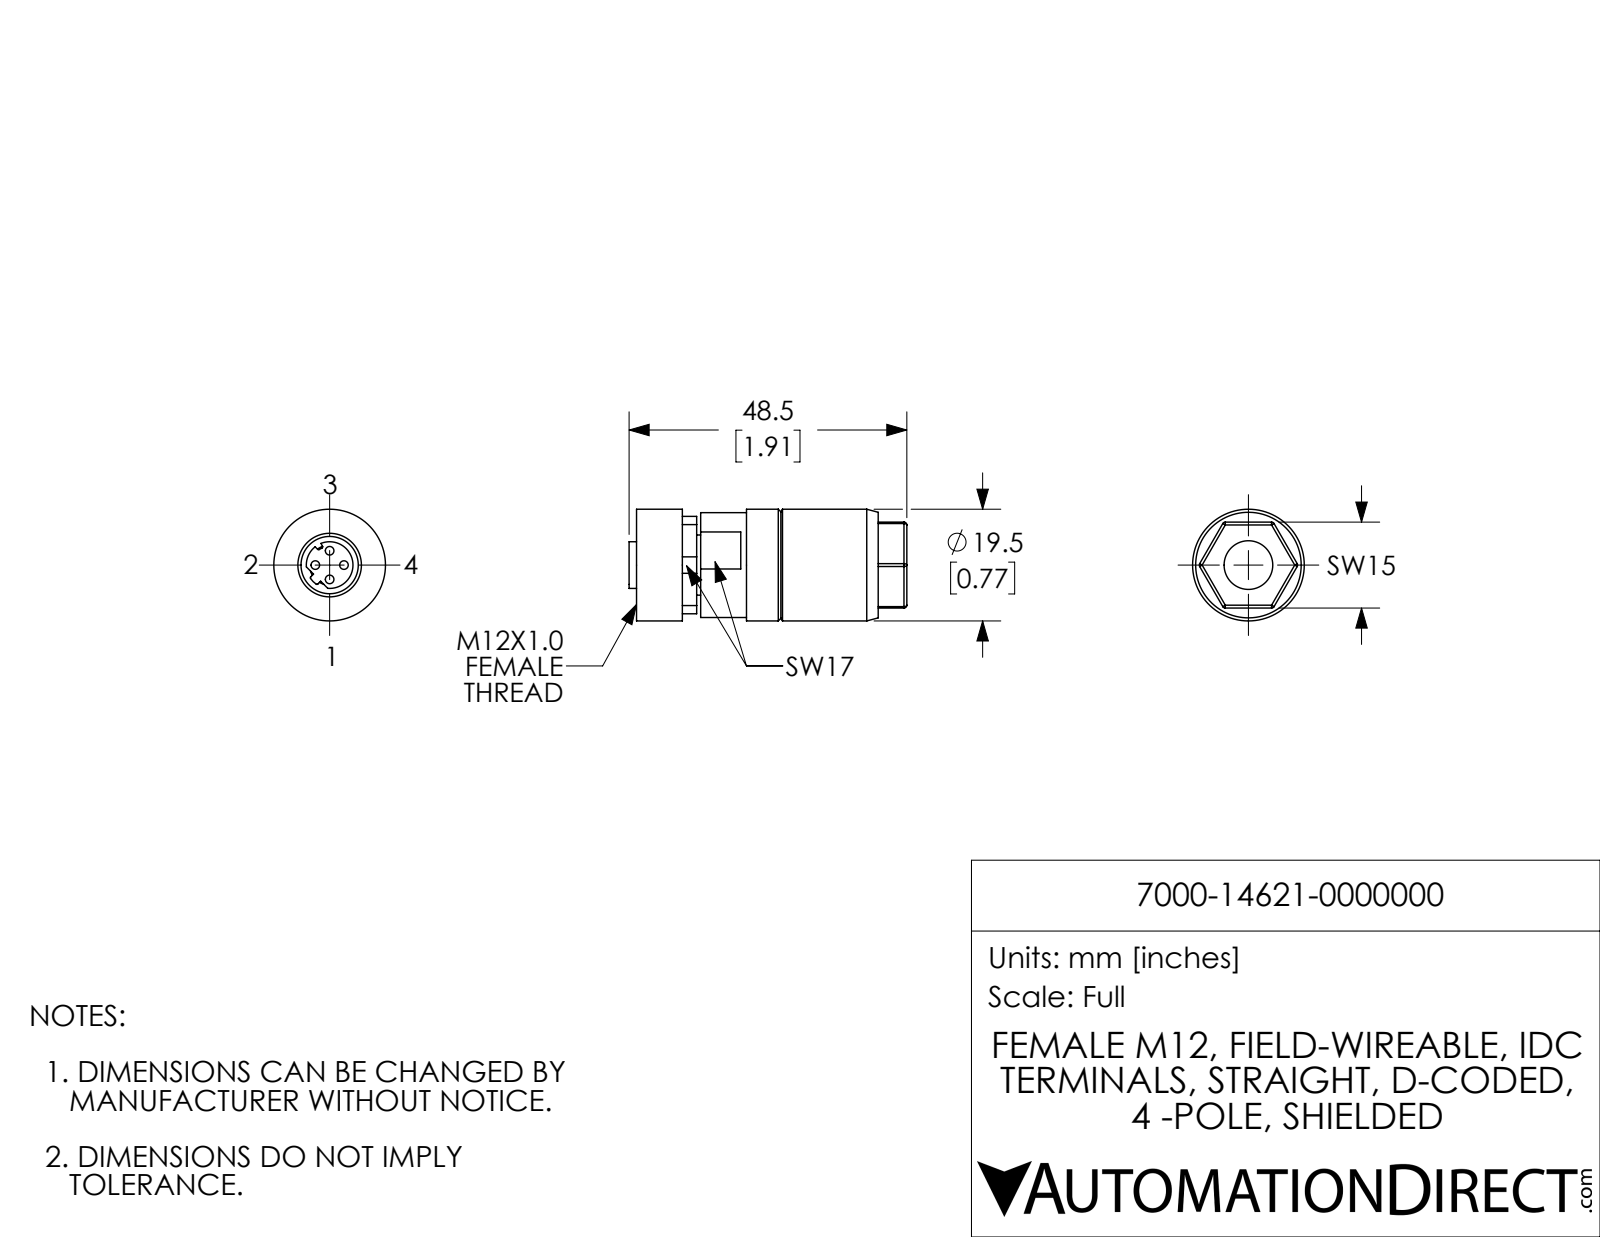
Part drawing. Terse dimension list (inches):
name: 7000-14621-0000000
written by: SolidWorks 2017 (AUTOMOTIVE_DESIGN)
unit: in
bodies: 1 solid, 113 faces (41 planar, 51 cylindrical, 21 other)
size: 1.909 × 0.768 × 0.768
volume: 0.741 in³; area: 7.25 in²
holes: 4× ⌀0.059, 1× ⌀0.335, 1× ⌀0.437
bosses: 1× ⌀0.768, 1× ⌀0.72, 1× ⌀0.413
rounds: 12× R0.02, 4× R0.008, 1× R0.008, 1× R0.16, 1× R0.358
face distances: 0.441, 0.413, 0.028, 0.315, 1.858, 1.445, 1.417, 1.543, 0.591, 0.039
hole spacings: 0.098, 0.139, 0.197
